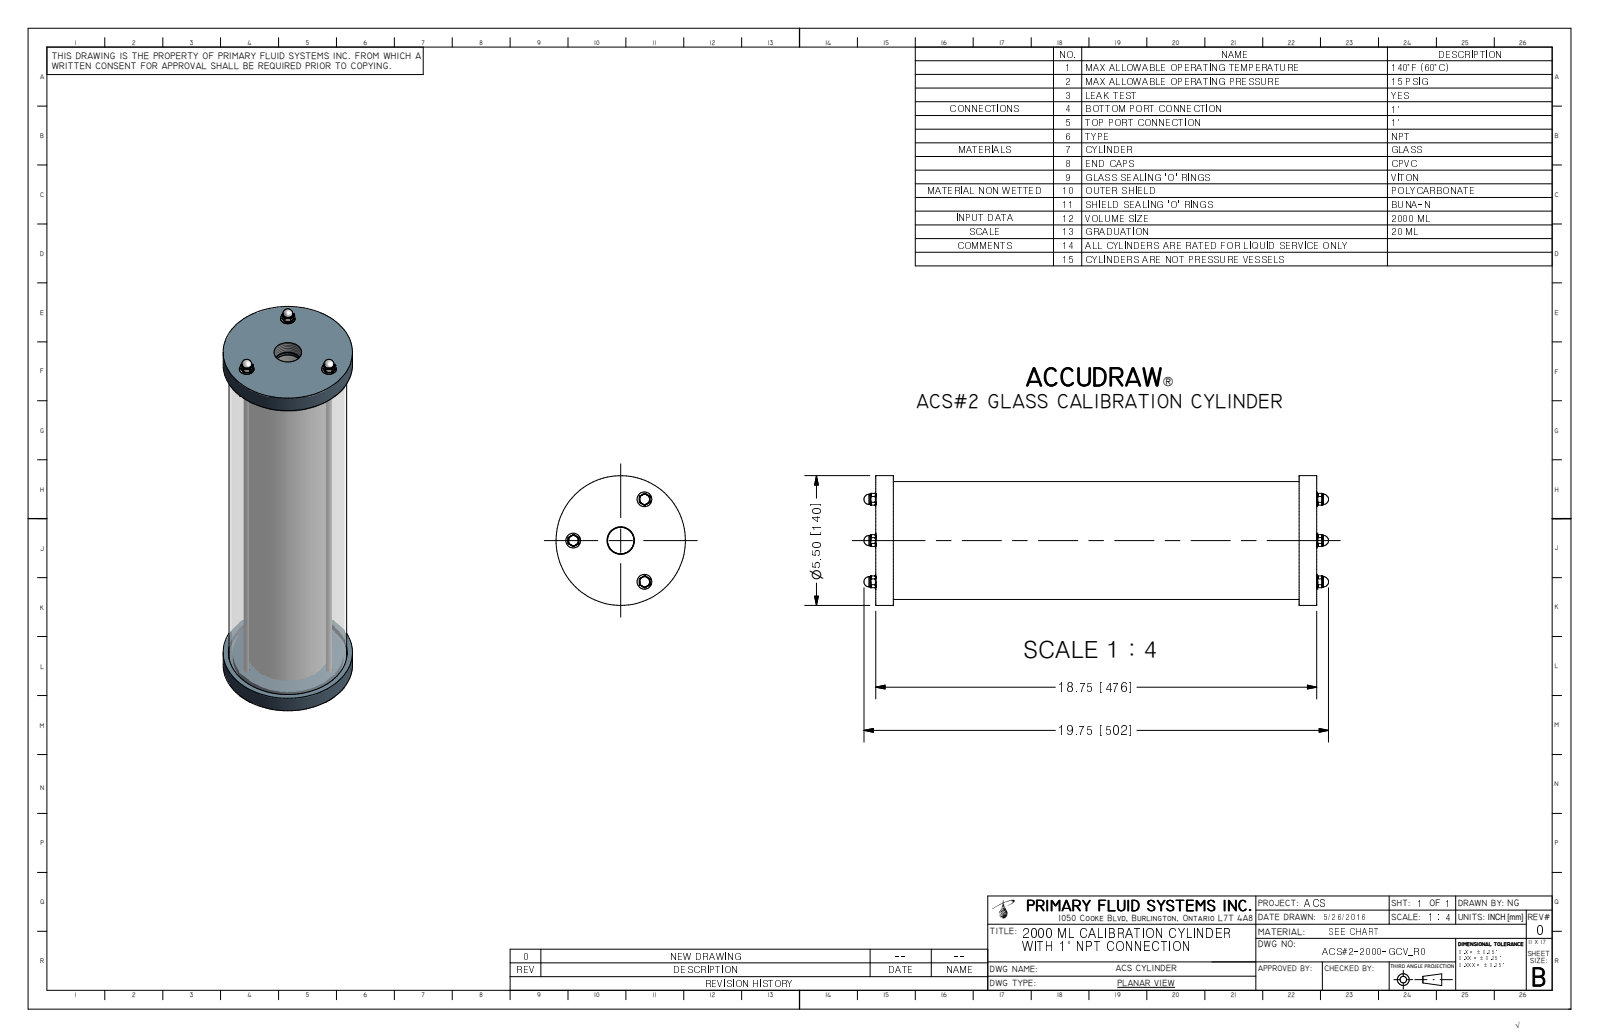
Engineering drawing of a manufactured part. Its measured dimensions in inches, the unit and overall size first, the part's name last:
Units: inches
Overall size (bounding box): 19.75 × 5.5 × 5.5
Round holes (diameter × count): ⌀0.18 ×3, ⌀0.266 ×3, ⌀0.281 ×3, ⌀3.15 ×1, ⌀3.4 ×1, ⌀4.75 ×1, ⌀5.05 ×1
Round bosses / shafts (diameter × count): ⌀0.625 ×3, ⌀0.25 ×3, ⌀5.5 ×1, ⌀5 ×1, ⌀4.7 ×1, ⌀3.346 ×1, ⌀3.1 ×1
Main face-to-face distances: 18, 0.75, 18.75, 17.25, 0.19, 17.71, 0.375, 0.1, 0.375, 17.9
Hole centre spacings: 2.019, 3.497
Volume: 85.47 in³ · Surface area: 1 117 in²
Bodies: 19 solids, 429 faces (38 planar, 41 cylindrical, 350 other)
Part name (STEP PRODUCT): ACS#2-2000-GCV_R0; ACS-3-2000-POLY_R3; ACS-2-2000-PC_R6; ACS-1-2000-A_R0 (+3 more)
STEP written by: Autodesk Inventor 2009 (AUTOMOTIVE_DESIGN)
